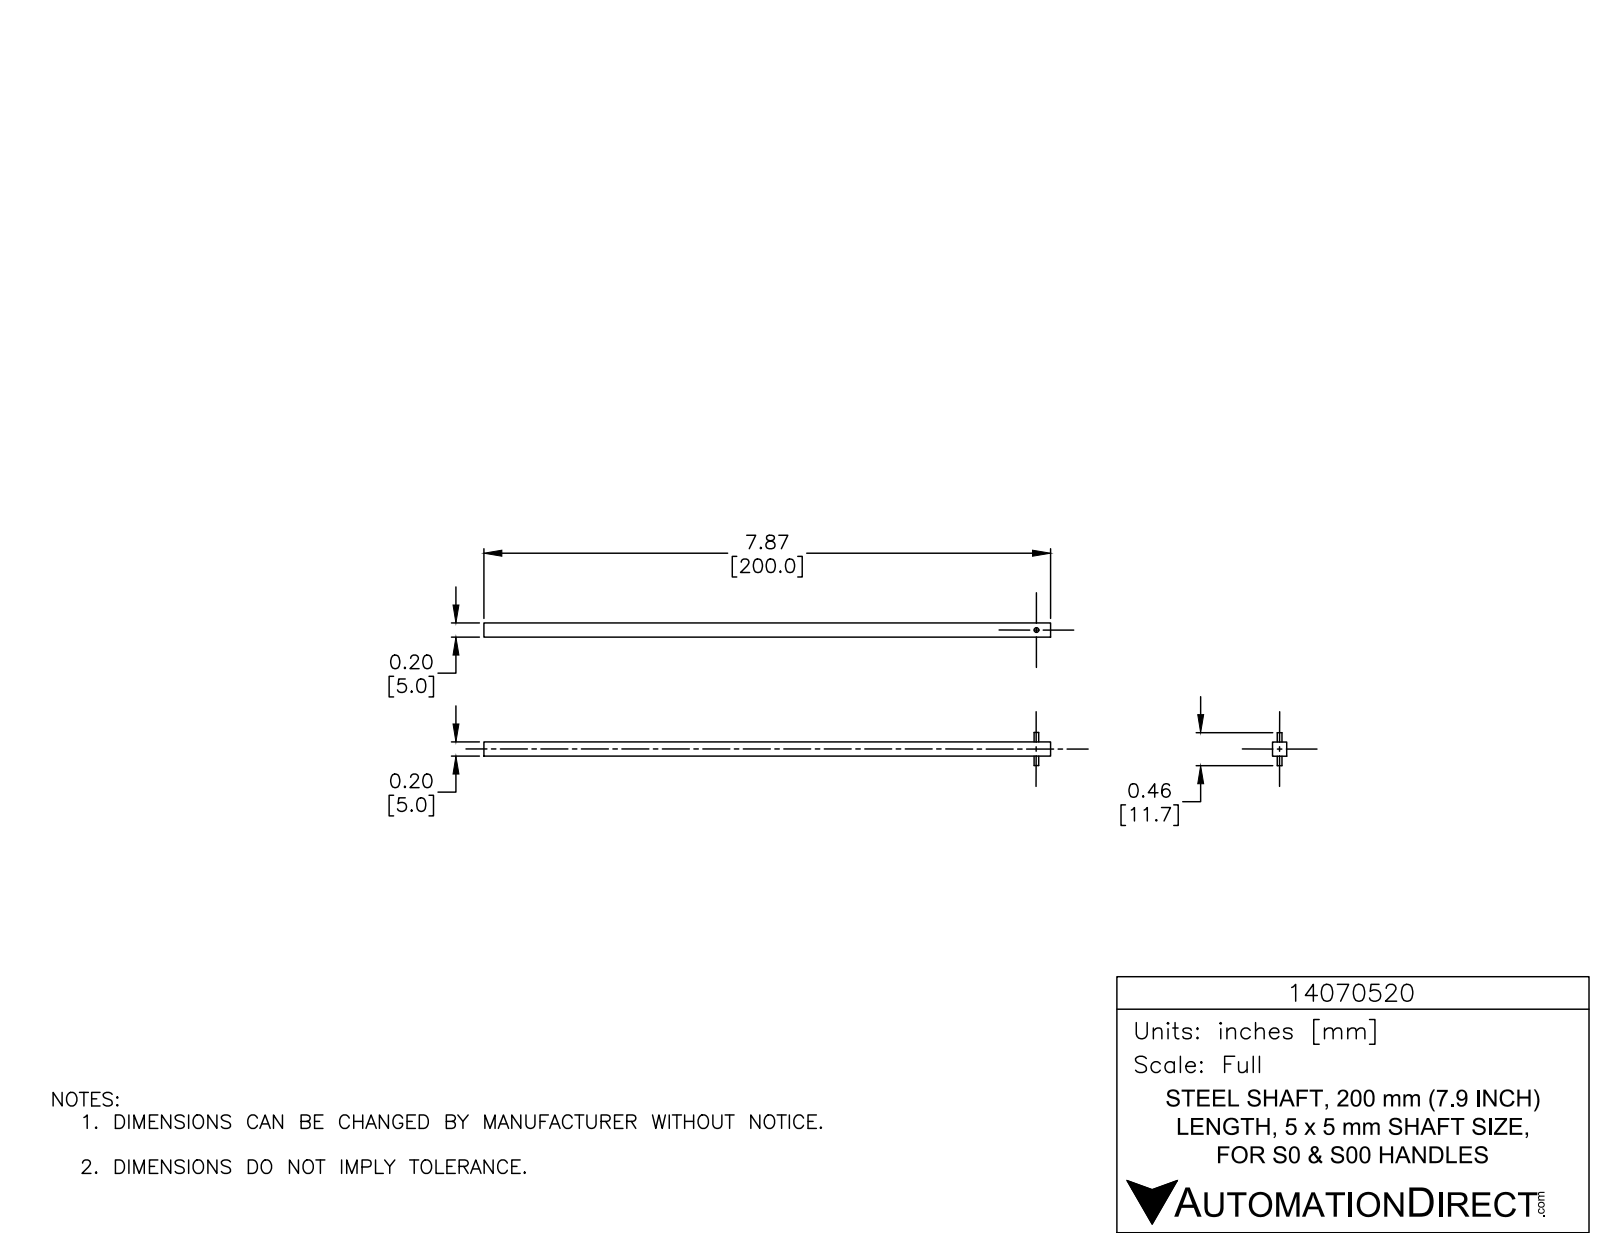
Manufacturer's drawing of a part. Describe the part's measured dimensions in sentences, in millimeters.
The part is named "14070520". Its 3-D file was written by "SolidWorks 2015 (AUTOMOTIVE_DESIGN)". It is 1 solid with 12 faces: 8 planar, 4 cylindrical and 0 other. Overall it measures 200 by 11.67 by 5 millimeters. Its volume is 5 015 cubic millimeters and its surface area 4 085 square millimeters. Round bosses or shafts: 1 of diameter 1.67. The main face-to-face distances are 5, 200, 3.33, 8.33, 11.66.
